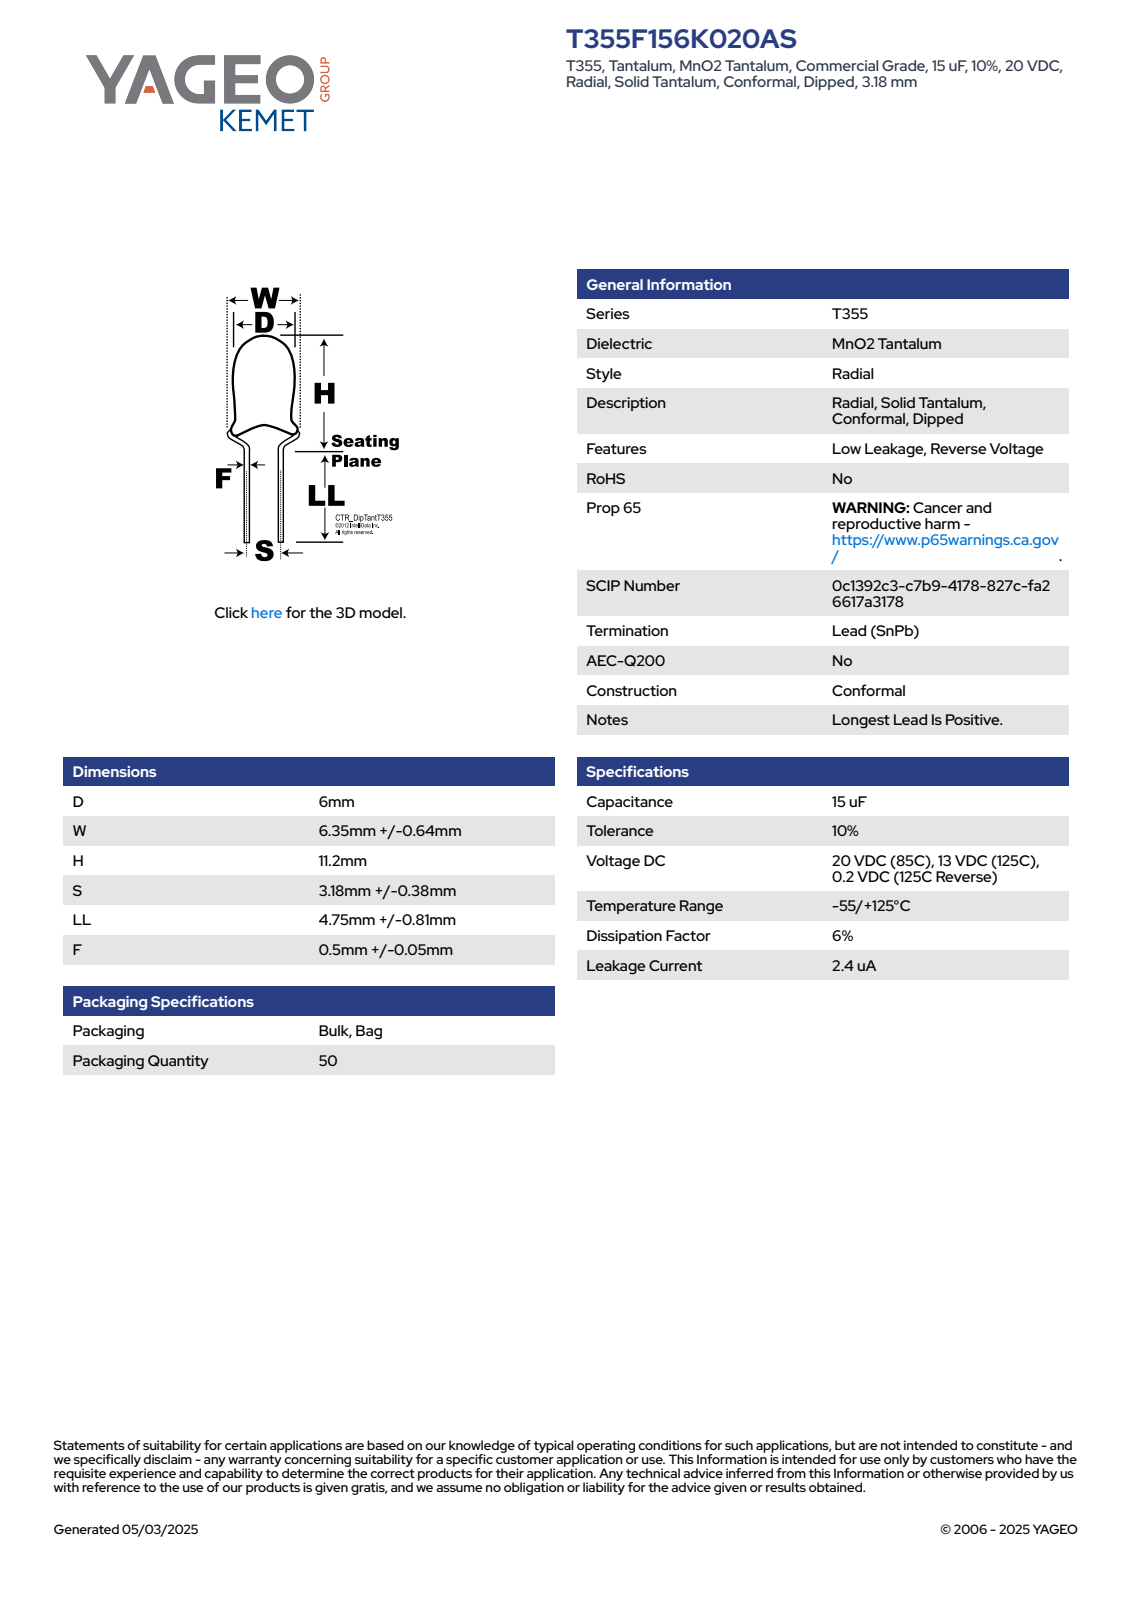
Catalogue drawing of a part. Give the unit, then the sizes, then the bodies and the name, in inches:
Units: inches
Overall size (bounding box): 0.66 × 0.275 × 0.236
Round bosses / shafts (diameter × count): ⌀0.236 ×1
Partial cylindrical surfaces — rounded edges, fillets, slot ends (radius × count): R0.118 ×1
Main face-to-face distances: 0.307, 0.352, 0.66, 0.522, 0.17, 0.138, 0.498, 0.146, 0.024, 0.162
Volume: 0.011 in³ · Surface area: 0.313 in²
Bodies: 1 solid, 100 faces (30 planar, 6 cylindrical, 64 other)
Part name (STEP PRODUCT): CTR_T355_D6W6.99H11.2S3.18LL5.56F0.55
STEP written by: SolidWorks 2021 (AUTOMOTIVE_DESIGN)
